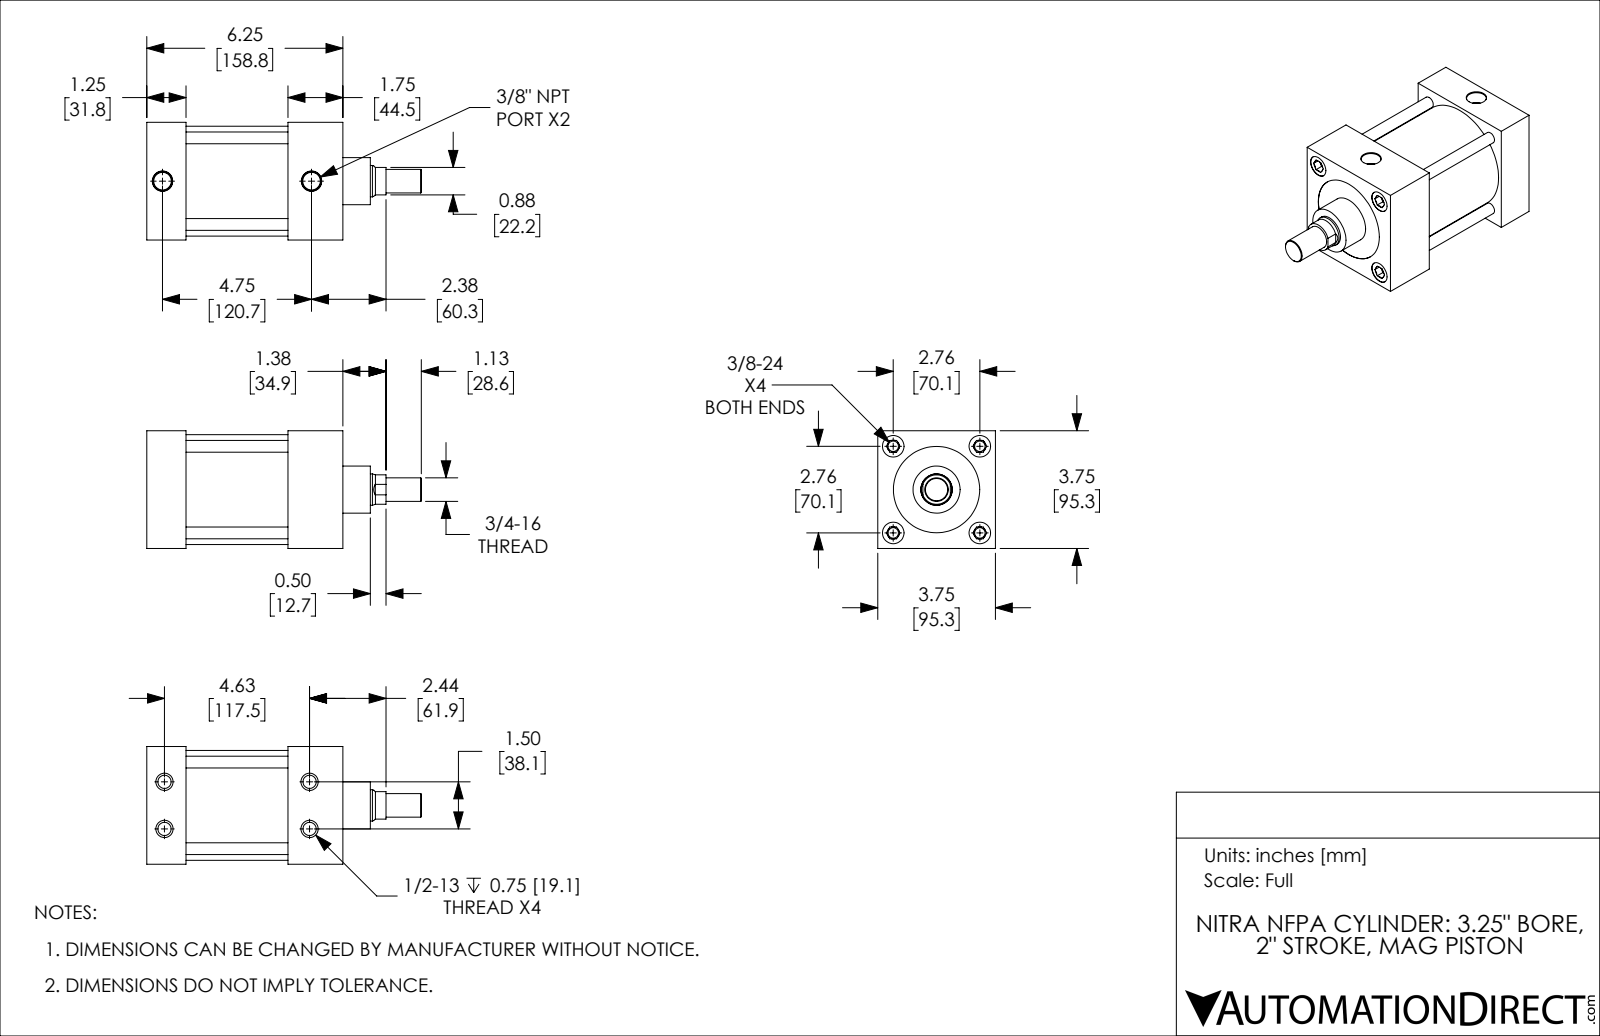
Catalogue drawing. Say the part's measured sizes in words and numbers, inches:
The part is named "D252020DT-M_BODY; D252020DT-M_PISTON_KK1; D252020DT-M". Its 3-D file was written by "SolidWorks 2019 (CONFIG_CONTROL_DESIGN)". It is 2 solids with 198 faces: 58 planar, 62 cylindrical and 78 other. Overall it measures 8.75 by 3.75 by 3.75 inches. Its volume is 60.04 cubic inches and its surface area 259.5 square inches. Round holes: 4 of diameter 0.332, 4 of diameter 0.422, 4 of diameter 0.687, 2 of diameter 0.562, 1 of diameter 1, 1 of diameter 2.75, 1 of diameter 3.251. Round bosses or shafts: 4 of diameter 0.375, 1 of diameter 3.501, 1 of diameter 3.249, 1 of diameter 1.5, 1 of diameter 0.999, 1 of diameter 0.75. Partial cylindrical surfaces (rounded edges, fillets, slot ends): 1 of radius 0.469. The main face-to-face distances are 1.25, 3.75, 4.5, 3.25, 3.75, 2.5, 2, 6.25, 5, 1.75. The hole center spacings are 0.753, 1.952, 2.76, 4.747, 1.5, 3.903, 4.625, 4.862.
